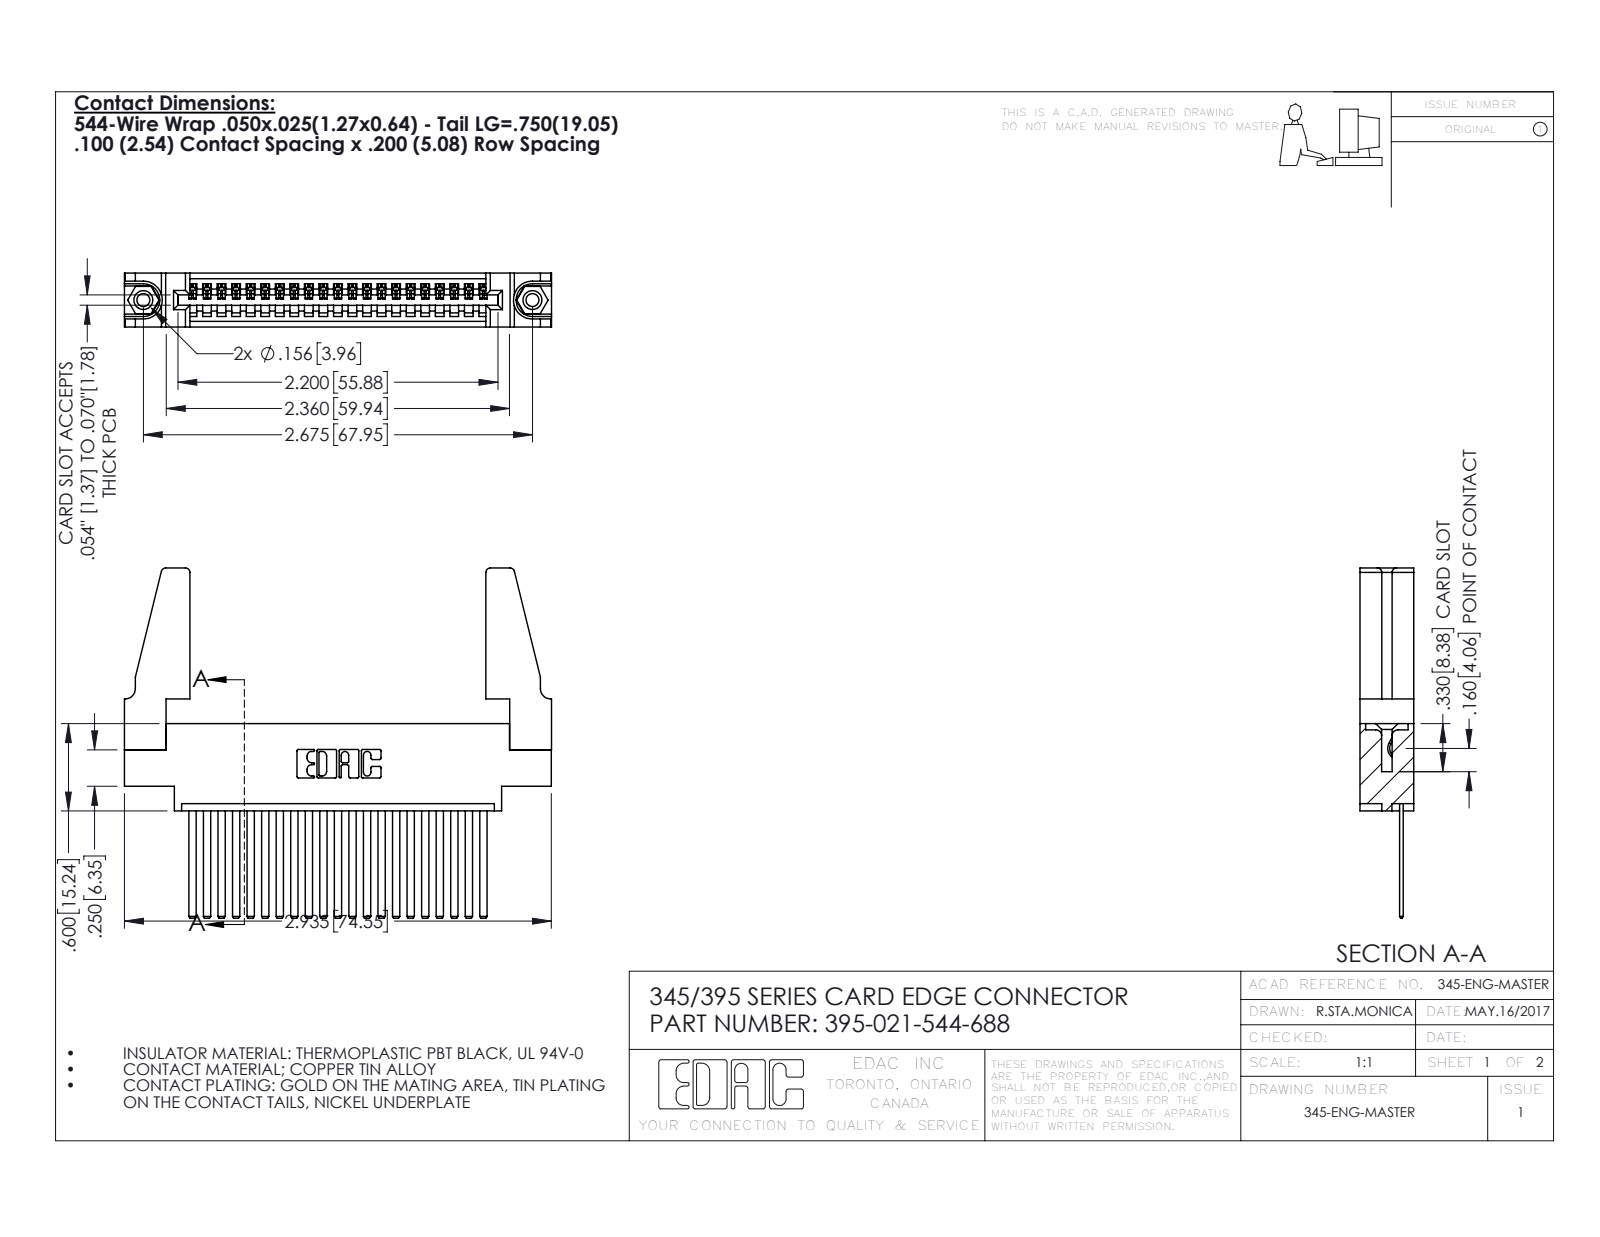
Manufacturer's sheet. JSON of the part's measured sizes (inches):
{"part_name": "345-250-001_345-250-001-102; 345-220-078_345-220-088; 395-021-544-688; 345 Part_0.170 Offset - 0.156 Dia-TH (+1 more)", "step_written_by": "SolidWorks 2016 (CONFIG_CONTROL_DESIGN)", "units": "inches", "bodies": {"solids": 26, "faces": 1346, "planar": 912, "cylindrical": 418, "other": 16}, "overall_size": [2.936, 2.407, 0.37], "volume_in3": 0.628, "surface_area_in2": 20.24, "round_holes": [[0.089, 2], [0.125, 2], [0.156, 2], [0.064, 1]], "round_bosses_or_shafts": [[0.155, 2]], "partial_cylinders_radius": [[0.006, 42], [0.01, 22], [0.03, 8], [0.007, 6], [0.031, 6], [0.026, 3], [0.031, 2], [0.04, 2]], "face_to_face_distances": [0.072, 0.298, 0.37, 0.098, 0.272, 0.025, 0.2, 0.225, 0.175, 0.15], "hole_center_spacings": [0.27, 2.441, 2.675]}
